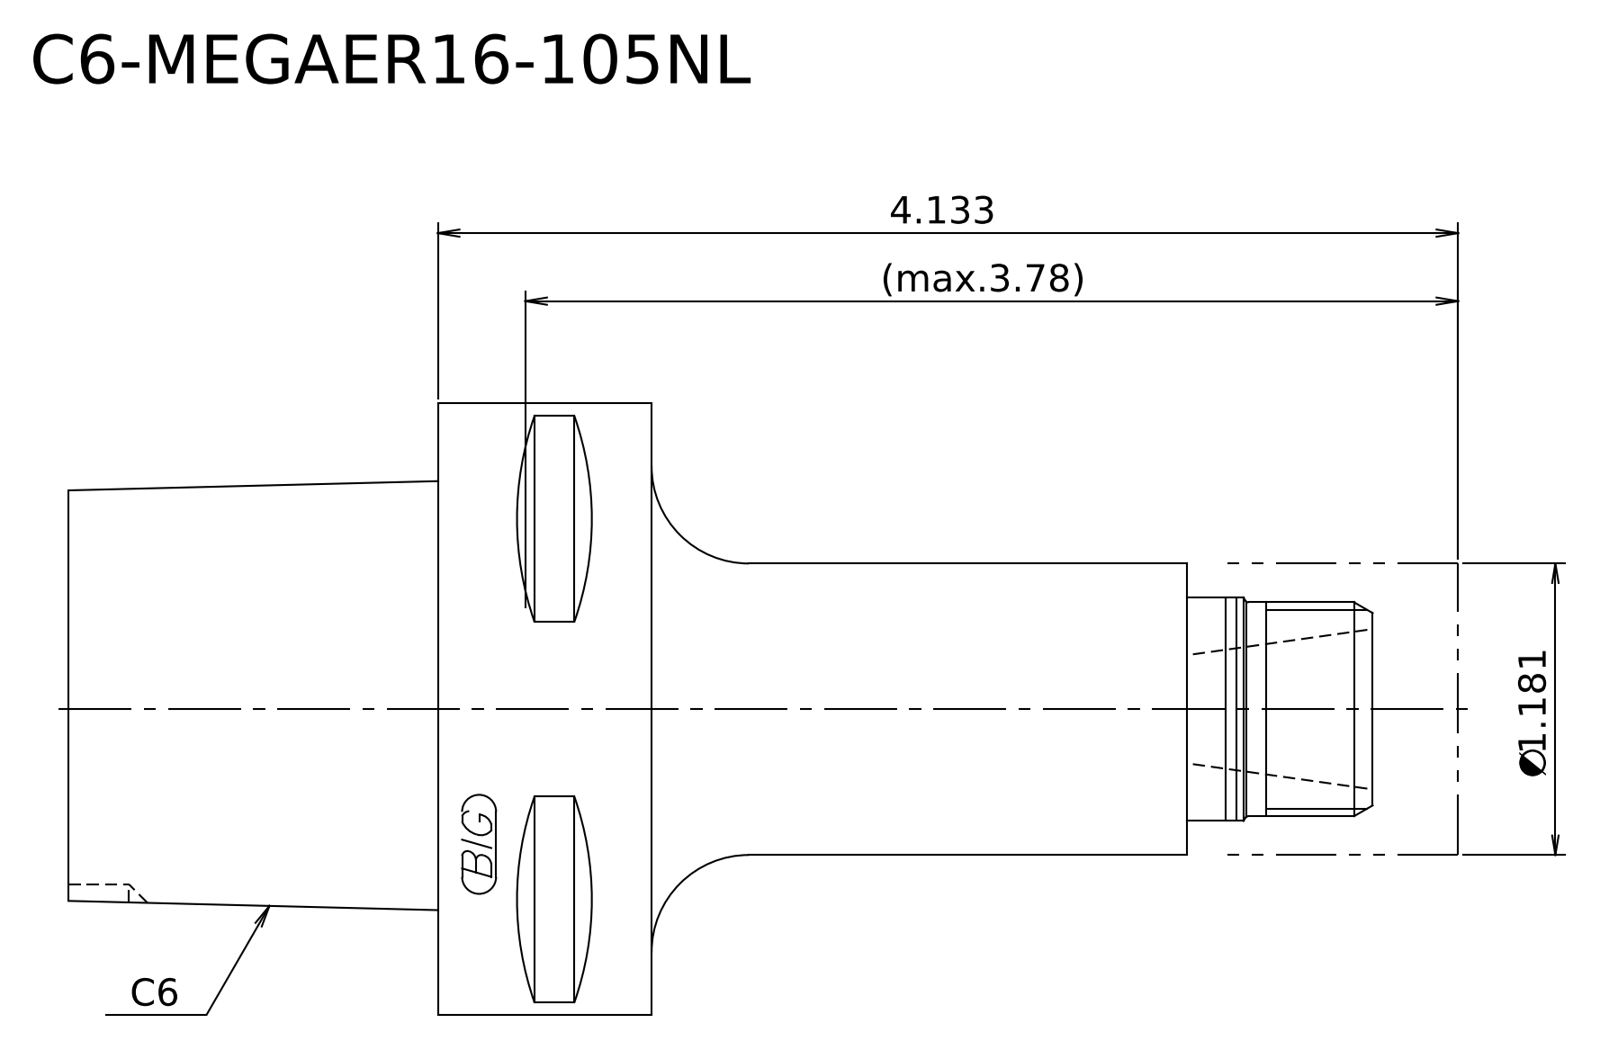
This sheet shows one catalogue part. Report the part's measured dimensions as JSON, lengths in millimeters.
{"step_written_by": "Kubotek KeyCreator 2011 V10.0.2 (22737) (automotive_design)", "units": "millimeters", "bodies": {"solids": 2, "faces": 18, "planar": 7, "cylindrical": 5, "other": 6}, "overall_size": [143, 63, 63], "volume_mm3": 193131, "surface_area_mm2": 25423, "round_bosses_or_shafts": [[63, 1], [30, 1], [23, 1], [22, 1]], "face_to_face_distances": [38, 22, 60, 58, 80, 118, 25, 83, 105, 143]}
